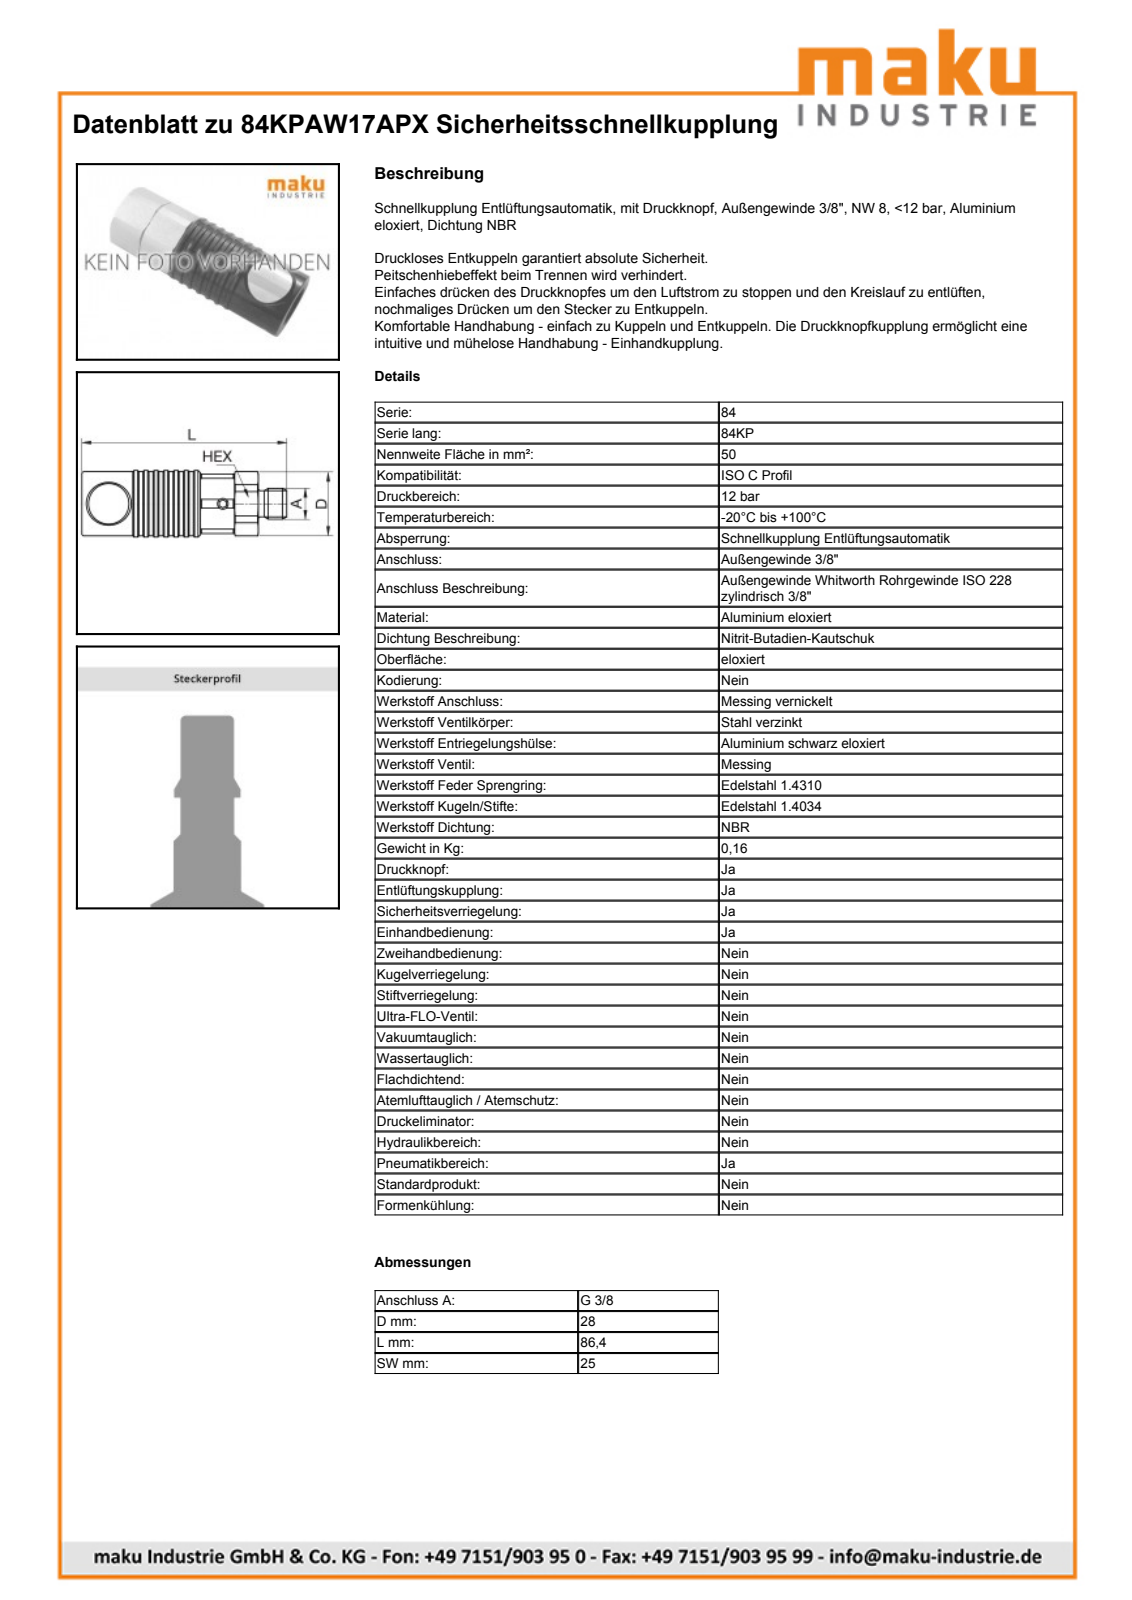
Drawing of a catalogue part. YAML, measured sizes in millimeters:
part_name: "84KPAW17APX"
step_written_by: "Autodesk Inventor 2019 (CONFIG_CONTROL_DESIGN)"
units: millimeters
bodies: {solids: 33, faces: 351, planar: 116, cylindrical: 124, other: 111}
overall_size: [85.4, 28, 28]
volume: 55279
surface_area: 32180
round_holes:
  - {diameter: 3.5, count: 2}
  - {diameter: 4, count: 2}
  - {diameter: 14, count: 2}
  - {diameter: 7.9, count: 1}
  - {diameter: 8, count: 1}
  - {diameter: 11.2, count: 1}
  - {diameter: 12, count: 1}
  - {diameter: 14.1, count: 1}
  - {diameter: 15.5, count: 1}
  - {diameter: 16.7, count: 1}
  - {diameter: 16.75, count: 1}
  - {diameter: 17.1, count: 1}
round_bosses_or_shafts:
  - {diameter: 28, count: 1}
  - {diameter: 27, count: 1}
  - {diameter: 25, count: 1}
  - {diameter: 23.33, count: 1}
  - {diameter: 23.3, count: 1}
  - {diameter: 23, count: 1}
  - {diameter: 21.11, count: 1}
  - {diameter: 19.7, count: 1}
partial_cylinders:
  - {radius: 5.53, count: 1}
  - {radius: 8.5, count: 1}
  - {radius: 9.3, count: 1}
  - {radius: 9.75, count: 1}
  - {radius: 13.5, count: 1}
  - {radius: 14.5, count: 1}
face_to_face_distances: [25, 64.4, 35.3, 29.1, 24.3, 6.4, 22.7, 41.7, 10, 11]
hole_center_spacings: [1.2, 1.3, 22, 26.1, 48.1]
